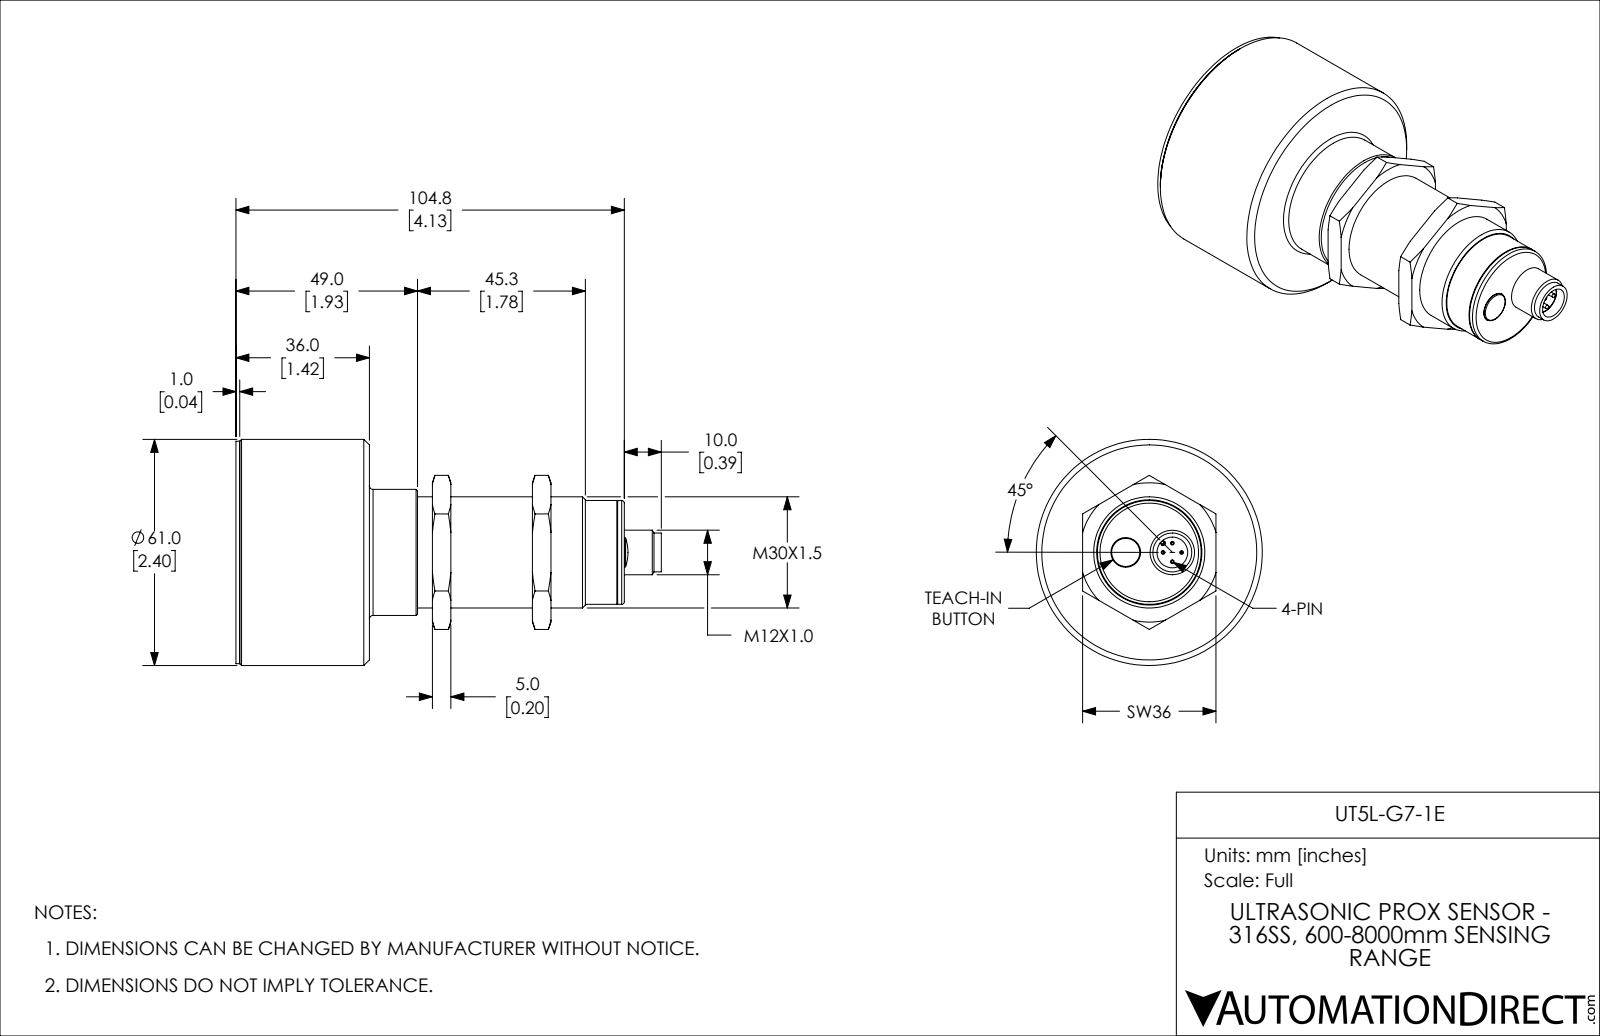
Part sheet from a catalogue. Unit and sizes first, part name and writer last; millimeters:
Units: millimetres
Overall size (bounding box): 114.8 × 61 × 61
Round holes (diameter × count): ⌀1.8 ×4, ⌀8 ×1, ⌀8.3 ×1, ⌀9.45 ×1, ⌀30 ×1, ⌀50 ×1
Round bosses / shafts (diameter × count): ⌀1 ×4, ⌀61 ×1, ⌀60 ×1, ⌀34 ×1, ⌀28.3 ×1, ⌀28 ×1, ⌀12 ×1, ⌀10.5 ×1
Partial cylindrical surfaces — rounded edges, fillets, slot ends (radius × count): R0.3 ×2, R0.6 ×1
Main face-to-face distances: 36, 35, 1, 13, 22, 14, 49, 67, 103, 102
Hole centre spacings: 2.5, 3.54, 5, 6.71, 12.82, 3.53, 3.72, 6.22
Volume: 194 457 mm³ · Surface area: 35 986 mm²
Bodies: 9 solids, 180 faces (52 planar, 57 cylindrical, 71 other)
Part name (STEP PRODUCT): UT5L-G7-1E
STEP written by: SolidWorks 2018 (AUTOMOTIVE_DESIGN)
